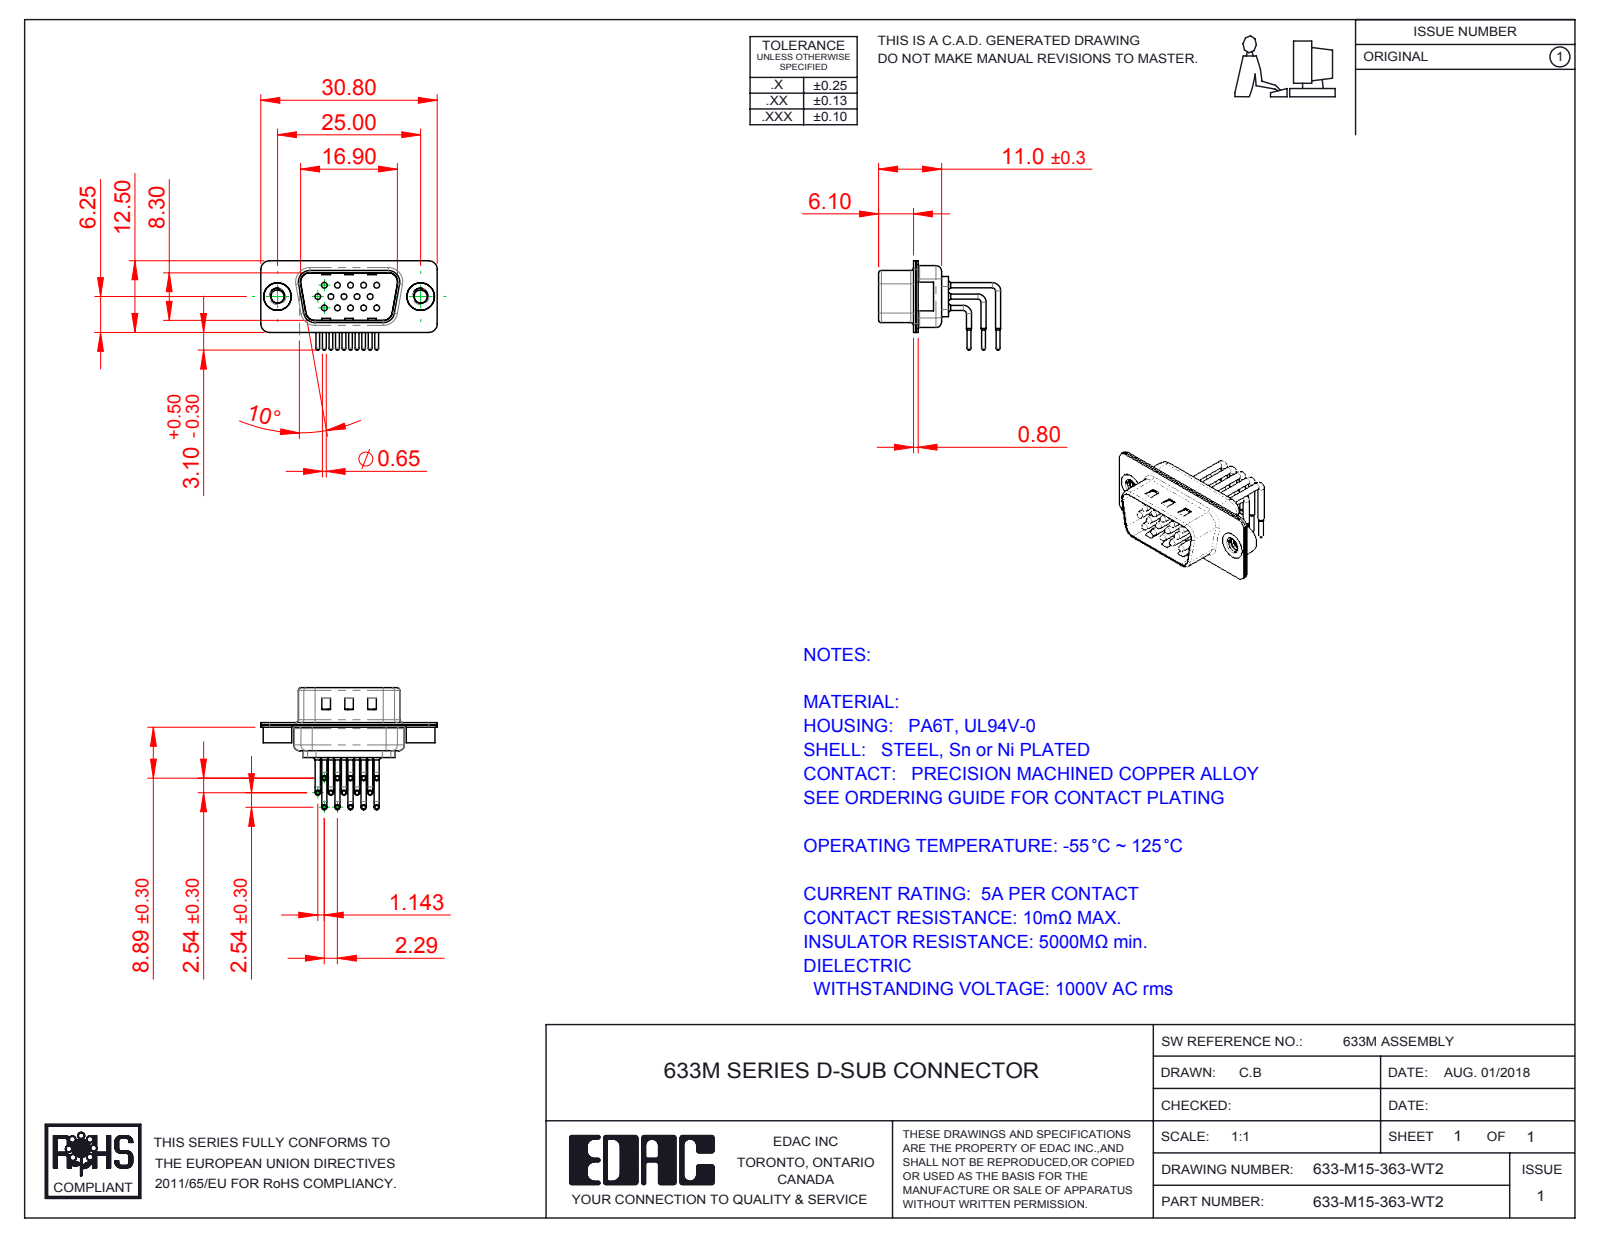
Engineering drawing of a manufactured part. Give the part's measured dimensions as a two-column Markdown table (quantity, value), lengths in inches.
| quantity | value |
| --- | --- |
| part name | 633M Shell Rear_15 Contacts; 633M Contact Row 2; 633M Shell Front_15 Contacts; 633M 4-40 Threaded Rivet (+4 more) |
| STEP written by | SolidWorks 2016 (CONFIG_CONTROL_DESIGN) |
| units | inches |
| bodies | 20 solids, 1954 faces (1067 planar, 669 cylindrical, 218 other) |
| overall size | 1.213 × 0.839 × 0.614 |
| volume | 0.089 in³ |
| surface area | 7.177 in² |
| round holes (diameter × count) | 0.039 × 15, 0.067 × 15, 0.079 × 15, 0.089 × 2, 0.157 × 2, 0.189 × 2 |
| round bosses / shafts (diameter × count) | 0.035 × 30, 0.059 × 15, 0.026 × 15, 0.197 × 2, 0.193 × 2 |
| partial cylindrical surfaces (radius × count) | 0.059 × 16, 0.04 × 15, 0.079 × 12, 0.02 × 8, 0.063 × 8, 0.01 × 4, 0.024 × 4, 0.026 × 4 |
| main face-to-face distances | 0.016, 0.033, 0.031, 0.376, 0.049, 0.409, 0.059, 0.343, 0.075, 0.014 |
| hole center spacings | 0.156, 0.09, 0.09, 0.18, 0.238, 0.27, 0.312, 0.238 |
